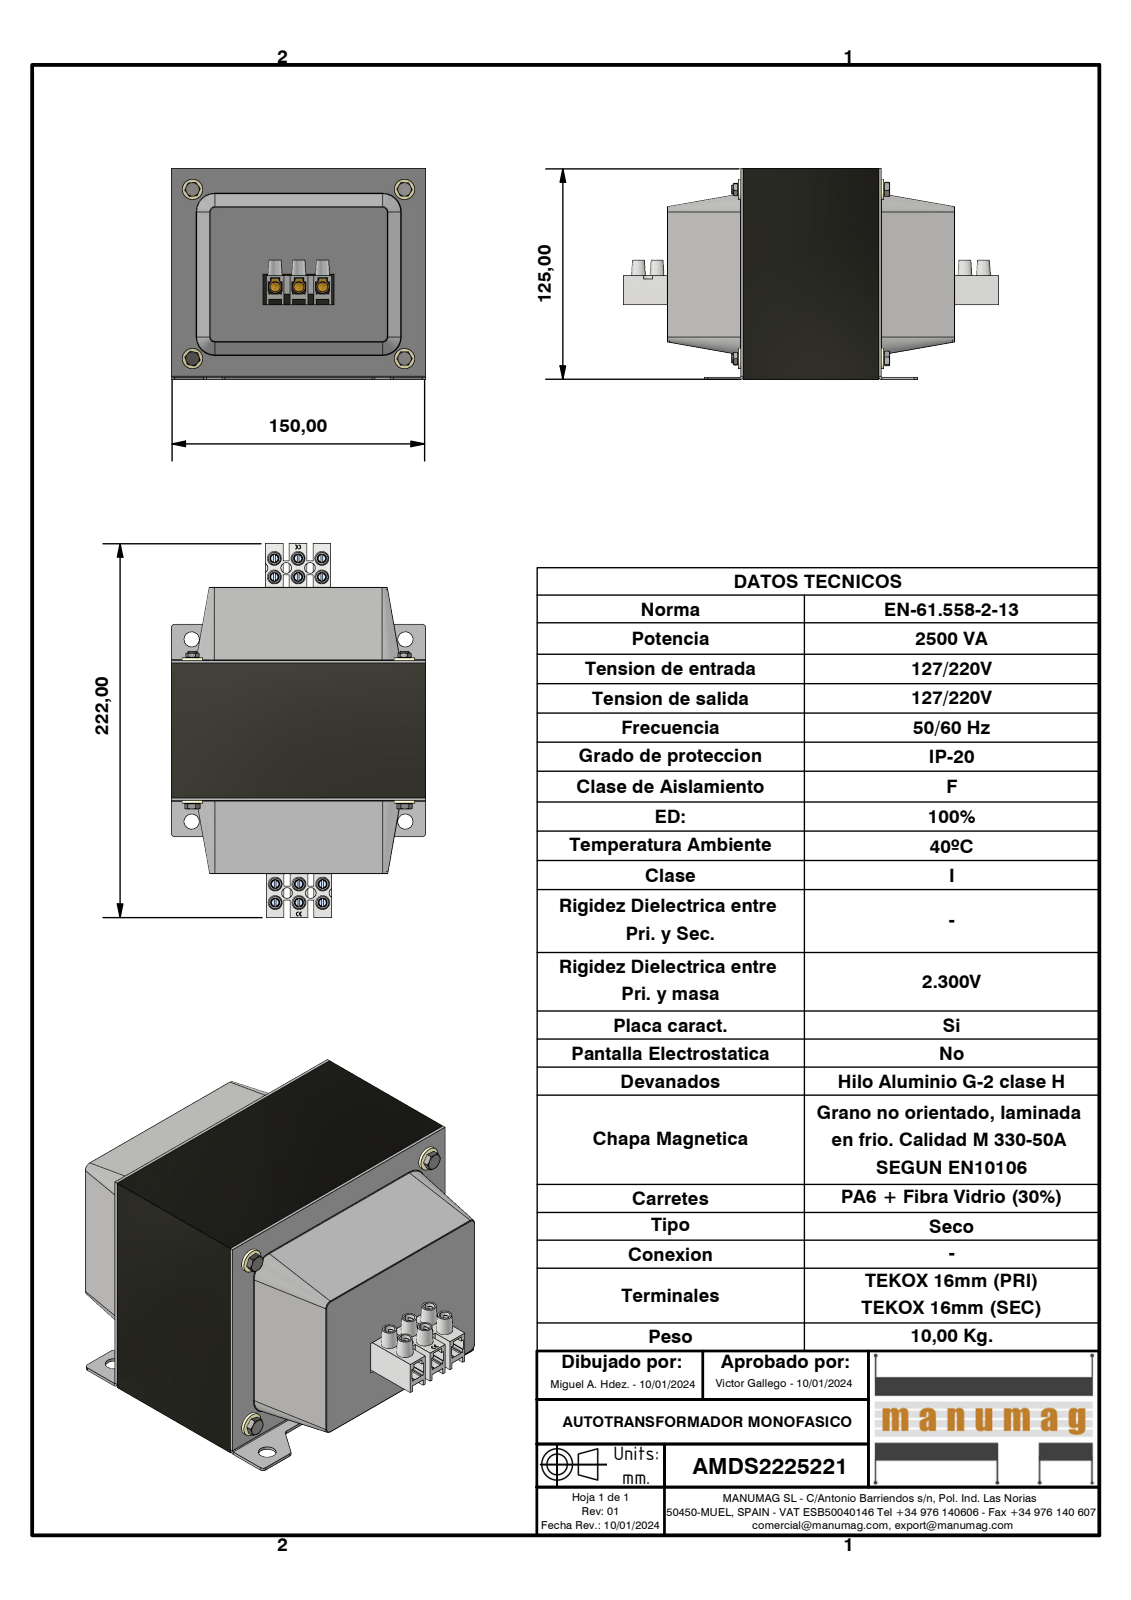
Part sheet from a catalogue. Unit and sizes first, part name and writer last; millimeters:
Units: millimetres
Overall size (bounding box): 222 × 150 × 125
Round holes (diameter × count): ⌀3.24 ×16, ⌀5.5 ×12, ⌀6 ×10, ⌀5 ×4, ⌀6.3 ×4, ⌀8 ×4, ⌀9 ×4
Round bosses / shafts (diameter × count): ⌀4 ×12, ⌀12 ×4, ⌀6.7 ×4, ⌀5.9 ×4, ⌀4.57 ×4
Partial cylindrical surfaces — rounded edges, fillets, slot ends (radius × count): R2.75 ×18, R0.38 ×16, R0.82 ×16, R2 ×14, R3 ×12, R0.81 ×8, R0.1 ×6, R0.22 ×6
Main face-to-face distances: 125, 1.5, 25, 43.5, 100, 80, 123.5, 50, 108.12, 75
Hole centre spacings: 14, 8.8, 9, 17.8, 11, 28, 193, 21.67
Volume: 1 271 000 mm³ · Surface area: 292 371 mm²
Bodies: 51 solids, 2194 faces (1488 planar, 286 cylindrical, 420 other)
Part name (STEP PRODUCT): AMDS2225221; centrador M5; DIN 934 - M4 x 0,7; TAPA RC50 VENTANA 3 ELEMENTOS 16 CON FICHAS (+8 more)
STEP written by: Autodesk Inventor 2023 (AUTOMOTIVE_DESIGN)
